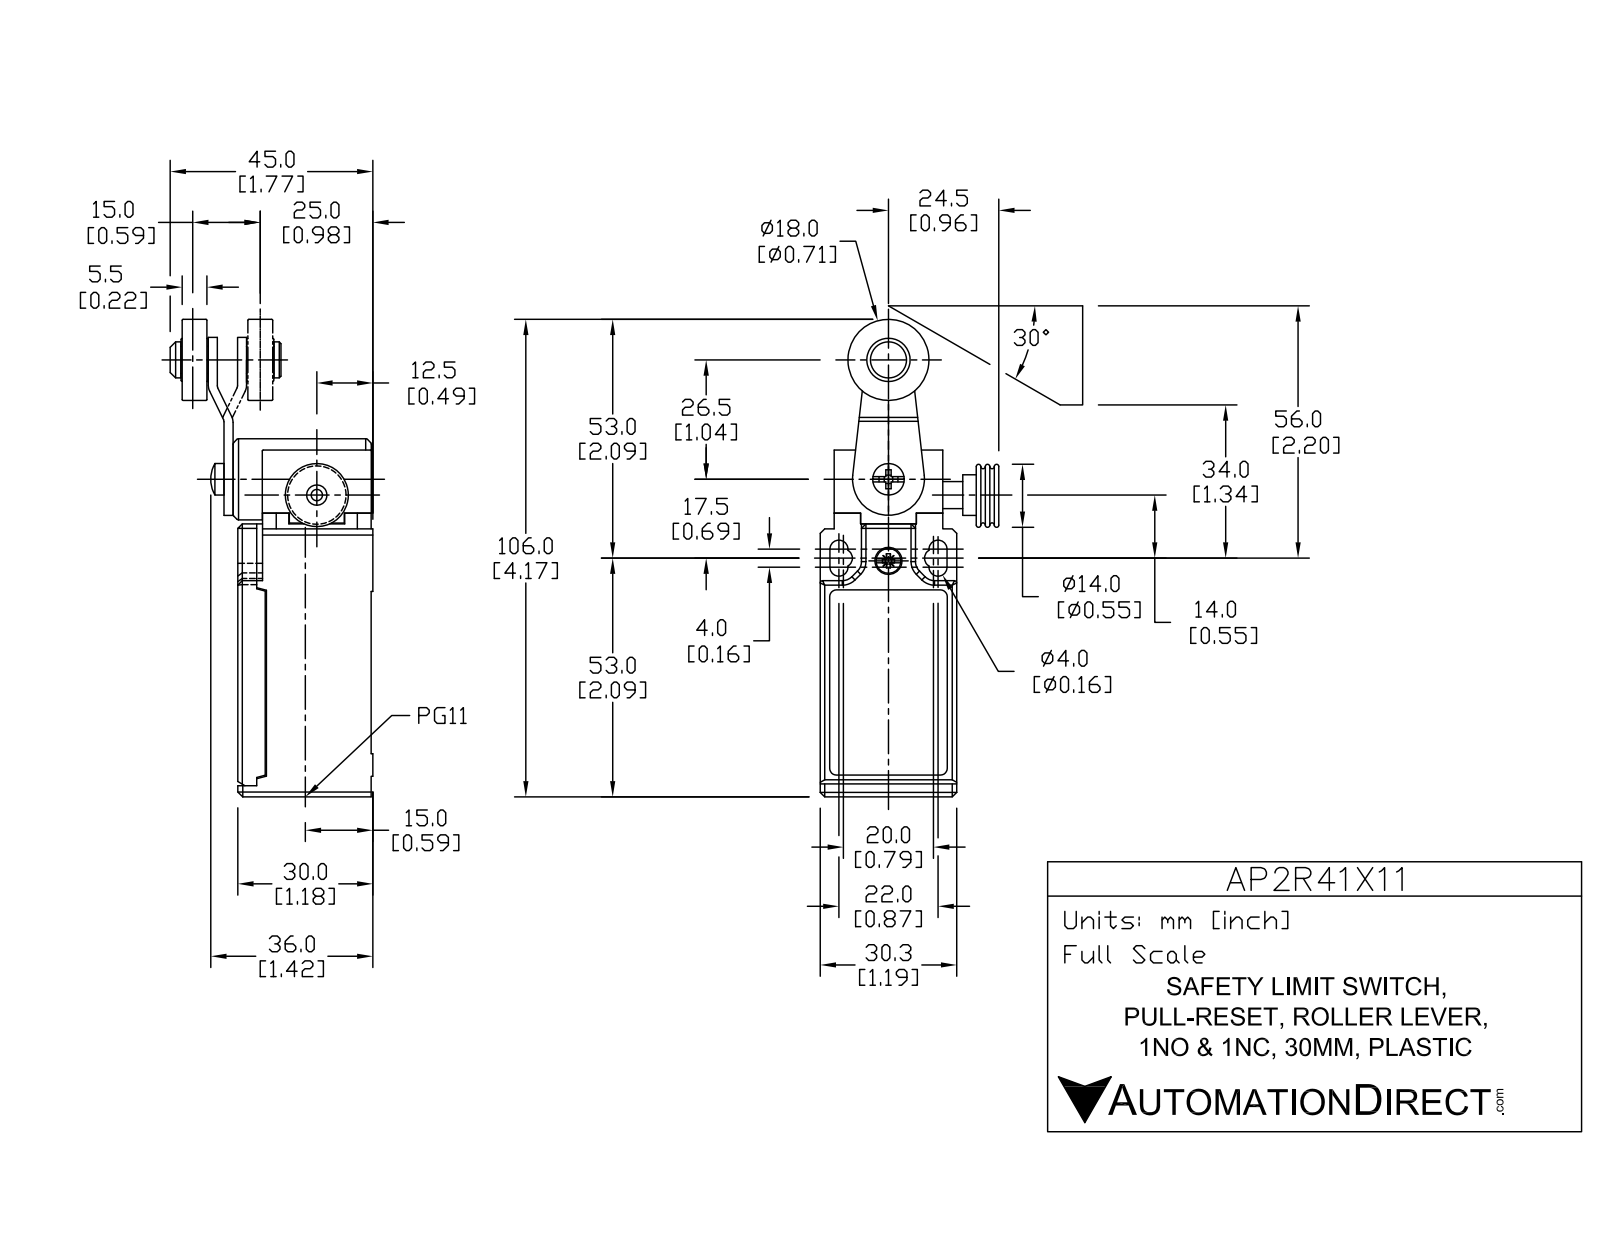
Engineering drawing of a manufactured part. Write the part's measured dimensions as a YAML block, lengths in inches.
part_name: "AP2R41X11"
step_written_by: "SolidWorks 2017 (AUTOMOTIVE_DESIGN)"
units: inches
bodies: {solids: 3, faces: 255, planar: 108, cylindrical: 84, other: 63}
overall_size: [4.232, 1.717, 1.543]
volume: 4.09
surface_area: 26.01
round_holes:
  - {diameter: 0.669, count: 1}
  - {diameter: 0.748, count: 1}
round_bosses_or_shafts:
  - {diameter: 0.22, count: 4}
  - {diameter: 0.217, count: 3}
  - {diameter: 0.709, count: 2}
  - {diameter: 0.587, count: 1}
  - {diameter: 0.531, count: 1}
  - {diameter: 0.386, count: 1}
  - {diameter: 0.374, count: 1}
  - {diameter: 0.315, count: 1}
partial_cylinders:
  - {radius: 0.02, count: 8}
  - {radius: 0.079, count: 6}
  - {radius: 0.118, count: 6}
  - {radius: 0.039, count: 4}
  - {radius: 0.197, count: 1}
  - {radius: 0.315, count: 1}
  - {radius: 0.394, count: 1}
  - {radius: 0.4, count: 1}
face_to_face_distances: [1.193, 1.165, 0.124, 1.069, 0.945, 0.236, 1.181, 0.016, 0.276, 2.444]
